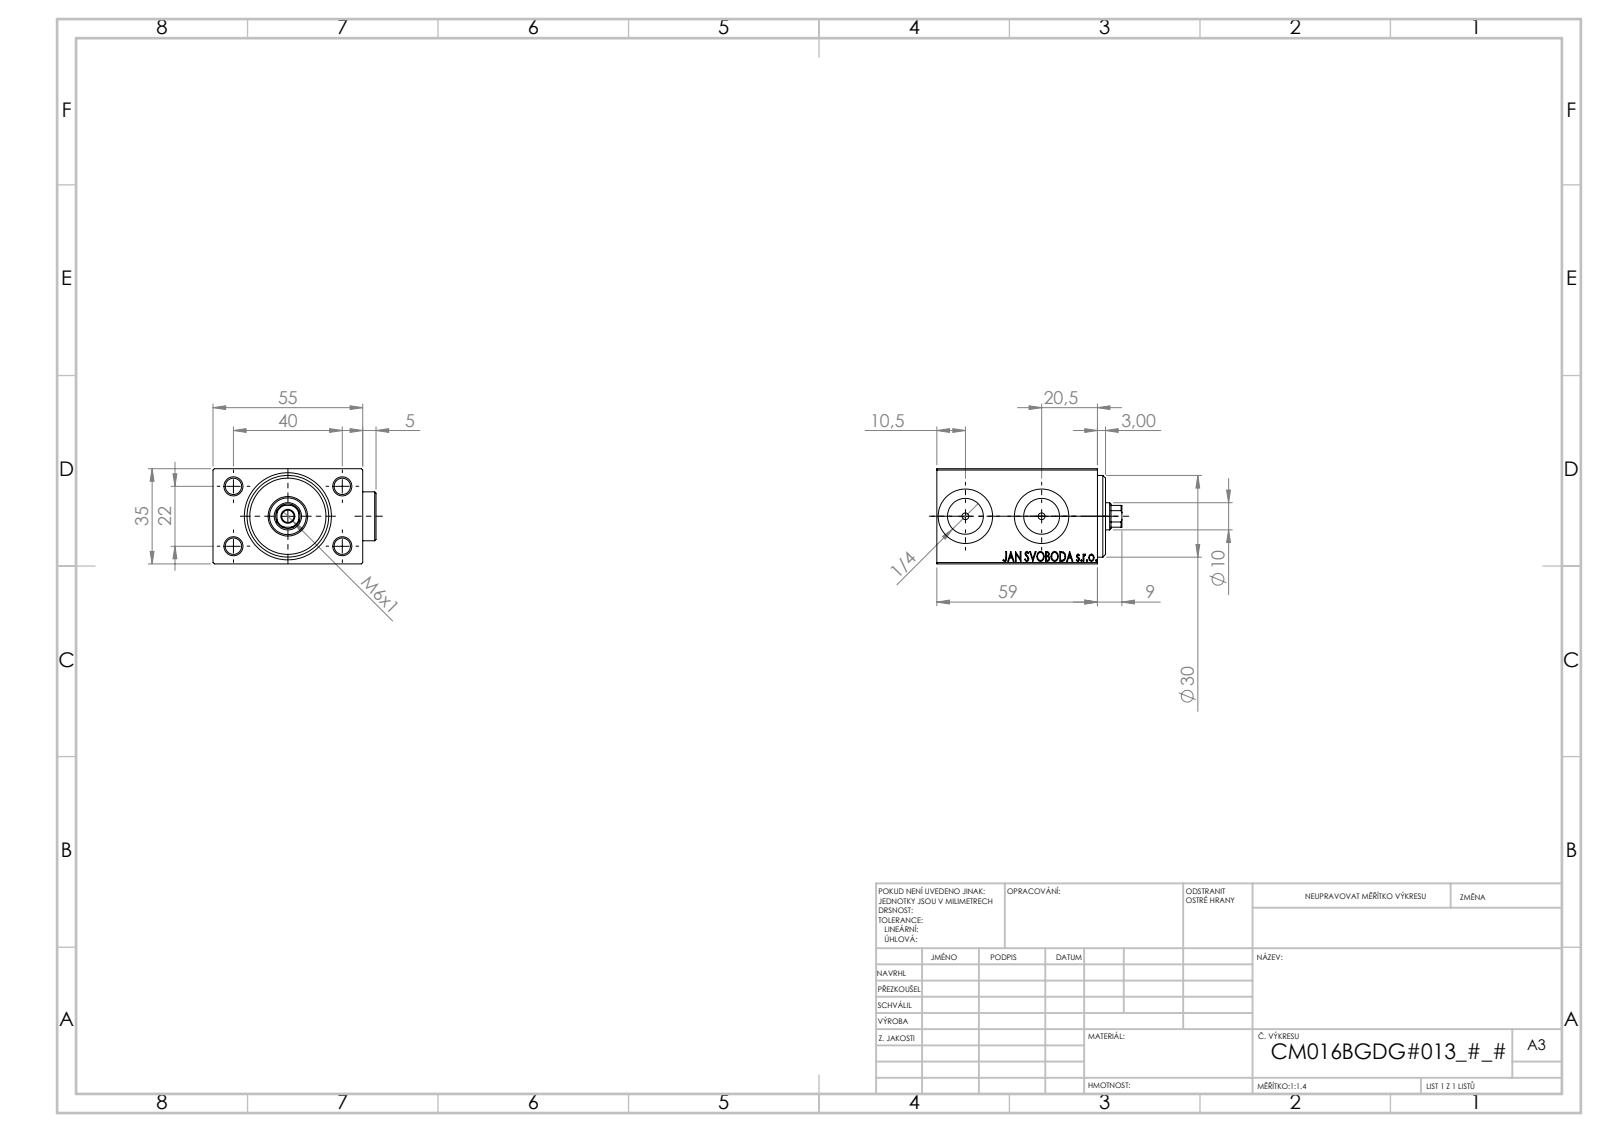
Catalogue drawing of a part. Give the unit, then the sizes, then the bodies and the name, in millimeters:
Units: millimetres
Overall size (bounding box): 68 × 59.9 × 35
Round holes (diameter × count): ⌀6 ×4, ⌀2.5 ×2, ⌀13.16 ×2, ⌀20 ×2, ⌀4.5 ×1, ⌀10 ×1, ⌀13.5 ×1, ⌀14.5 ×1, ⌀16 ×1, ⌀18 ×1, ⌀30 ×1
Round bosses / shafts (diameter × count): ⌀18 ×2
Partial cylindrical surfaces — rounded edges, fillets, slot ends (radius × count): R4.5 ×1
Main face-to-face distances: 35, 5, 55, 54, 54.9, 59, 3, 8, 62, 54.8
Hole centre spacings: 22.83, 22, 40, 45.65, 28
Volume: 106 580 mm³ · Surface area: 28 644 mm²
Bodies: 5 solids, 937 faces (437 planar, 70 cylindrical, 430 other)
Part name (STEP PRODUCT): V450CM_B_VCP; V450CM_B_Body; V450CM_VC_B; Zatka_OIL_PORT
STEP written by: SolidWorks 2019 (CONFIG_CONTROL_DESIGN)
